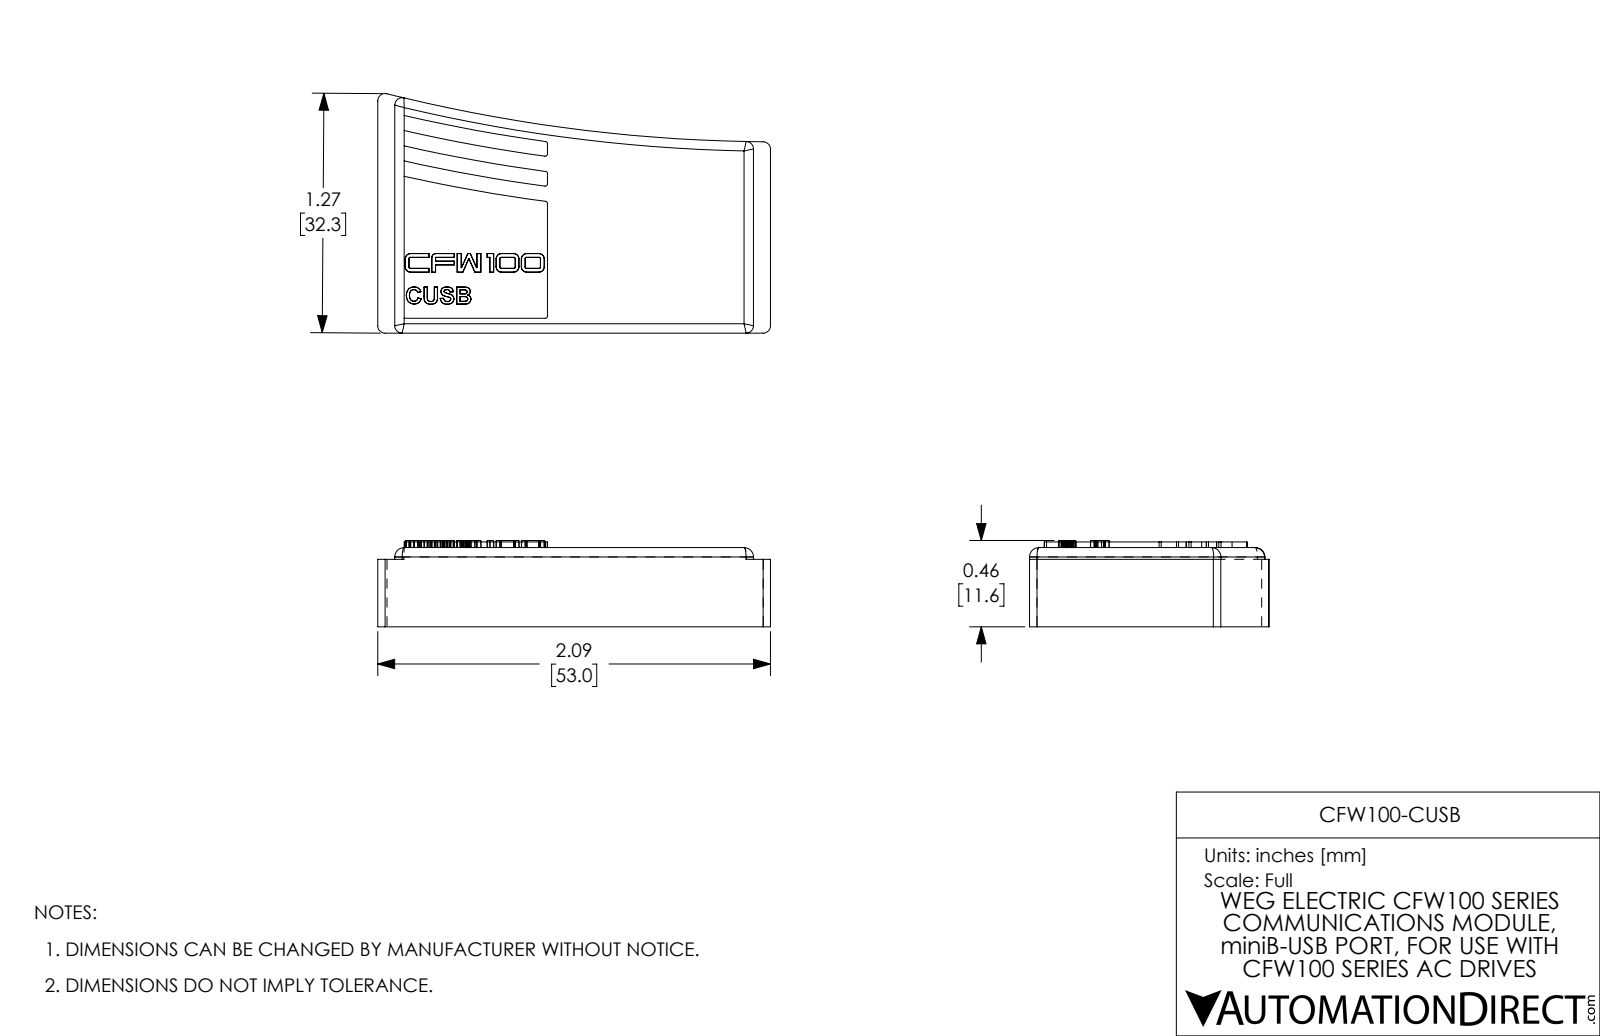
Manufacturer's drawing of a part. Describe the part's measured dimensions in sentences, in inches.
The part is named "IGS CFW100-CUSB Source but wrong b1". Its 3-D file was written by "SolidWorks 2017 (AUTOMOTIVE_DESIGN)". It is 1 solid with 258 faces: 239 planar, 14 cylindrical and 5 other. Overall it measures 2.087 by 1.272 by 0.654 inches. Its volume is 1.419 cubic inches and its surface area 8.554 square inches. Partial cylindrical surfaces (rounded edges, fillets, slot ends): 11 of radius 0.039, 1 of radius 8.52. The main face-to-face distances are 0.642, 0.091, 1.996, 2.087, 1.906, 0.358, 0.283, 0.654, 0.295, 0.018.
